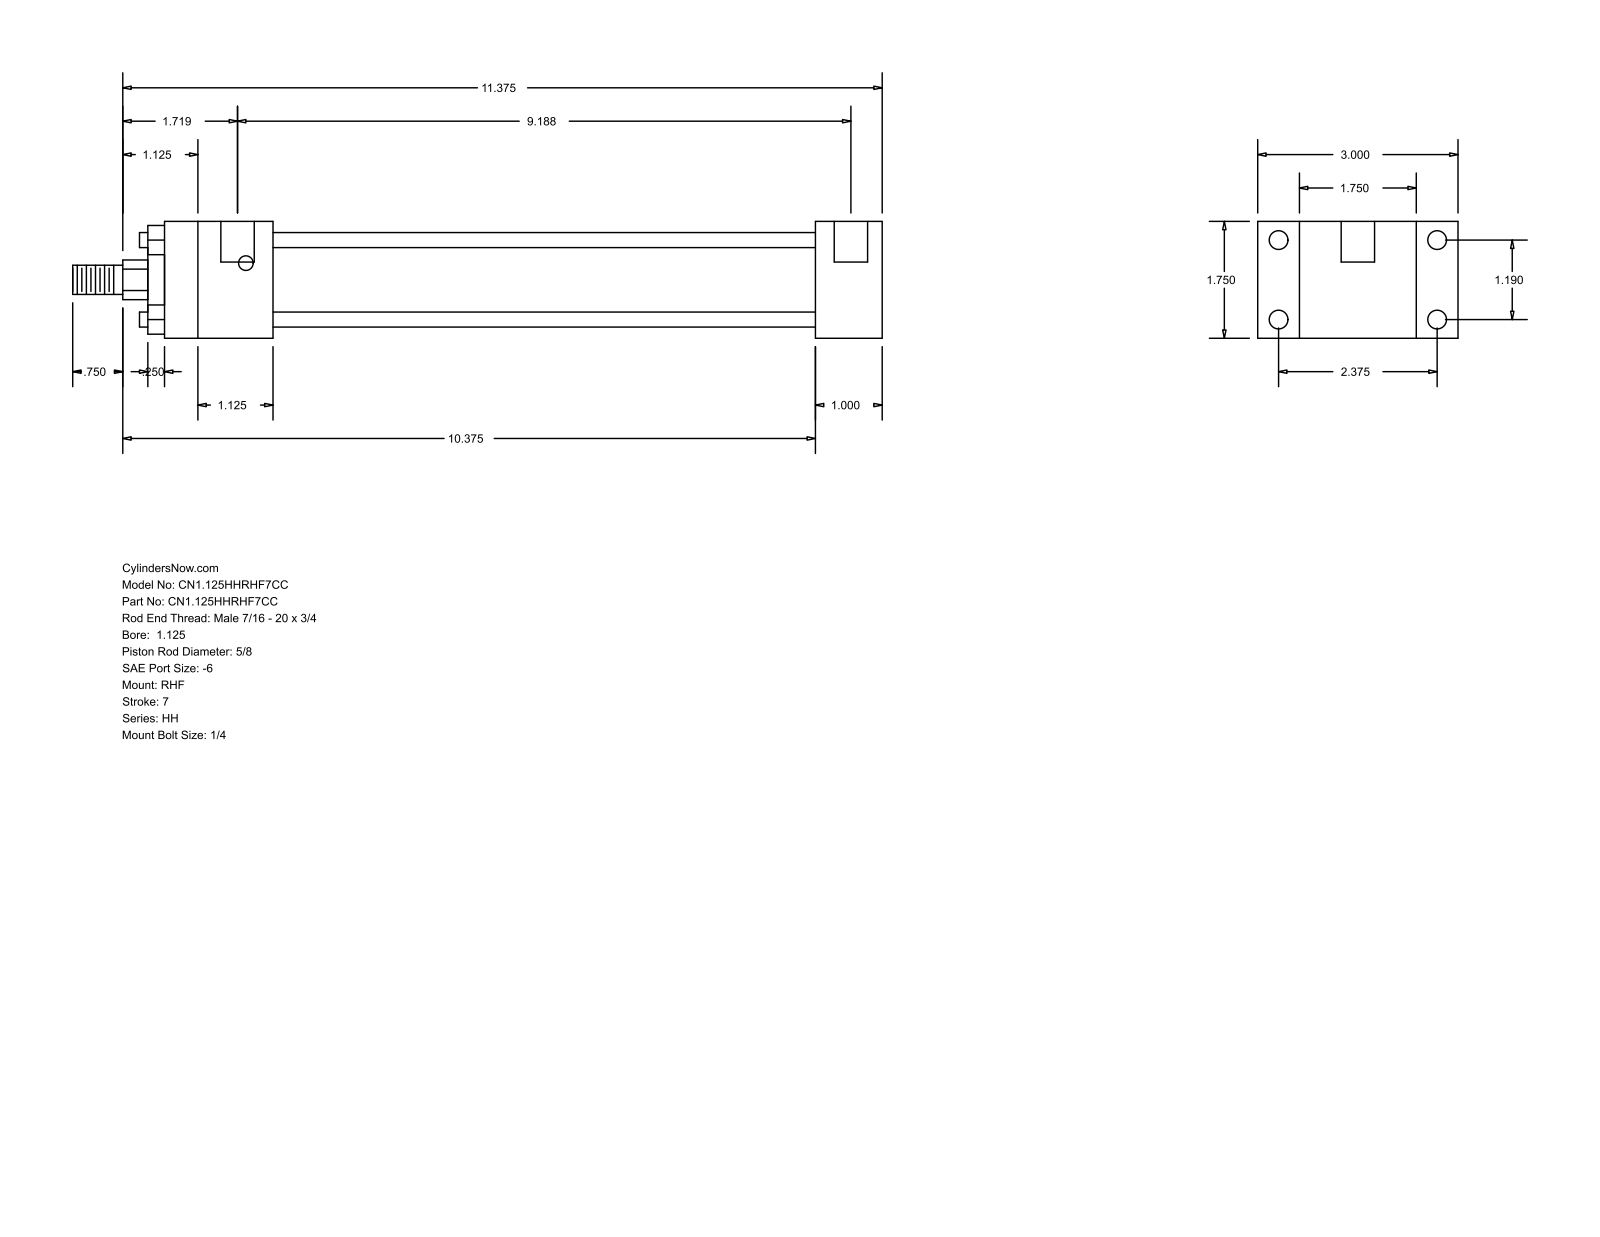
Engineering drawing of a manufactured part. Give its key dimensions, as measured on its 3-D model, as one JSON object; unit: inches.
{"part_name": "HH_RHF__0112_0.625", "step_written_by": "GSSL Pune (CONFIG_CONTROL_DESIGN)", "units": "inches", "bodies": {"solids": 0, "faces": 88, "planar": 60, "cylindrical": 28, "other": 0}, "overall_size": [12.125, 3, 1.75], "round_holes": [[0.219, 4], [0.281, 4], [0.5, 2]], "round_bosses_or_shafts": [[0.225, 4], [1.375, 1], [1.125, 1], [0.625, 1], [0.437, 1]], "partial_cylinders_radius": [[0.297, 1]], "face_to_face_distances": [1.75, 0.625, 2.375, 1, 3, 8.125, 9.125, 1.625, 9.75, 10.75], "hole_center_spacings": [1.19, 2.375, 2.656, 9.063, 0.125, 9.187]}
